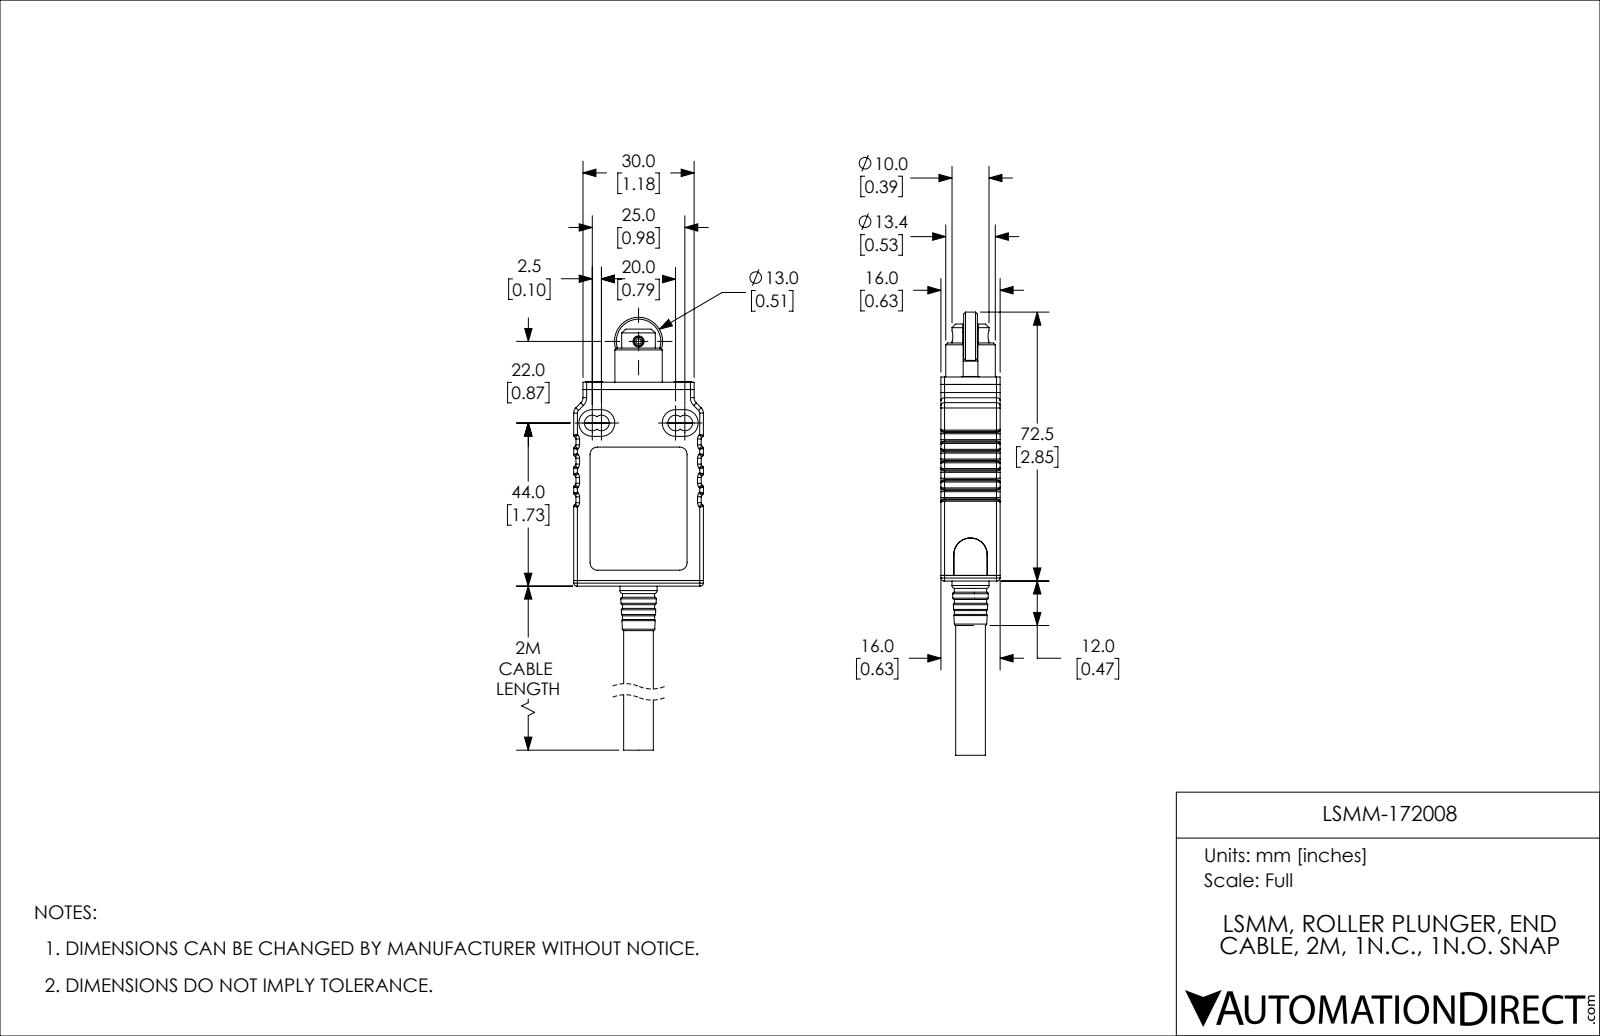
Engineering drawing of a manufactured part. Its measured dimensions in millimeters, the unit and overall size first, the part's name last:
Units: millimetres
Overall size (bounding box): 119.5 × 35 × 16
Round holes (diameter × count): ⌀2 ×2, ⌀2.5 ×2, ⌀2.6 ×2, ⌀1.5 ×1, ⌀2.4 ×1, ⌀3 ×1, ⌀3.2 ×1, ⌀3.3 ×1, ⌀4 ×1, ⌀5.4 ×1, ⌀8 ×1, ⌀9 ×1
Round bosses / shafts (diameter × count): ⌀4.7 ×2, ⌀14.7 ×1, ⌀13.4 ×1, ⌀13 ×1, ⌀11 ×1, ⌀10.6 ×1, ⌀10 ×1, ⌀9.8 ×1
Partial cylindrical surfaces — rounded edges, fillets, slot ends (radius × count): R0.5 ×74, R1 ×52, R2 ×8, R0.8 ×4, R2.1 ×4, R3.6 ×4, R0.3 ×3, R0.2 ×2
Main face-to-face distances: 1.5, 15.7, 14.5, 1, 1.2, 14.2, 2.5, 2, 15.4, 13
Hole centre spacings: 12, 24
Volume: 17 957 mm³ · Surface area: 19 072 mm²
Bodies: 12 solids, 719 faces (249 planar, 305 cylindrical, 165 other)
Part name (STEP PRODUCT): 170-LSPM-Roller Plunger-Bottom Cable (STEP format)
STEP written by: SolidWorks 2013 (CONFIG_CONTROL_DESIGN)
